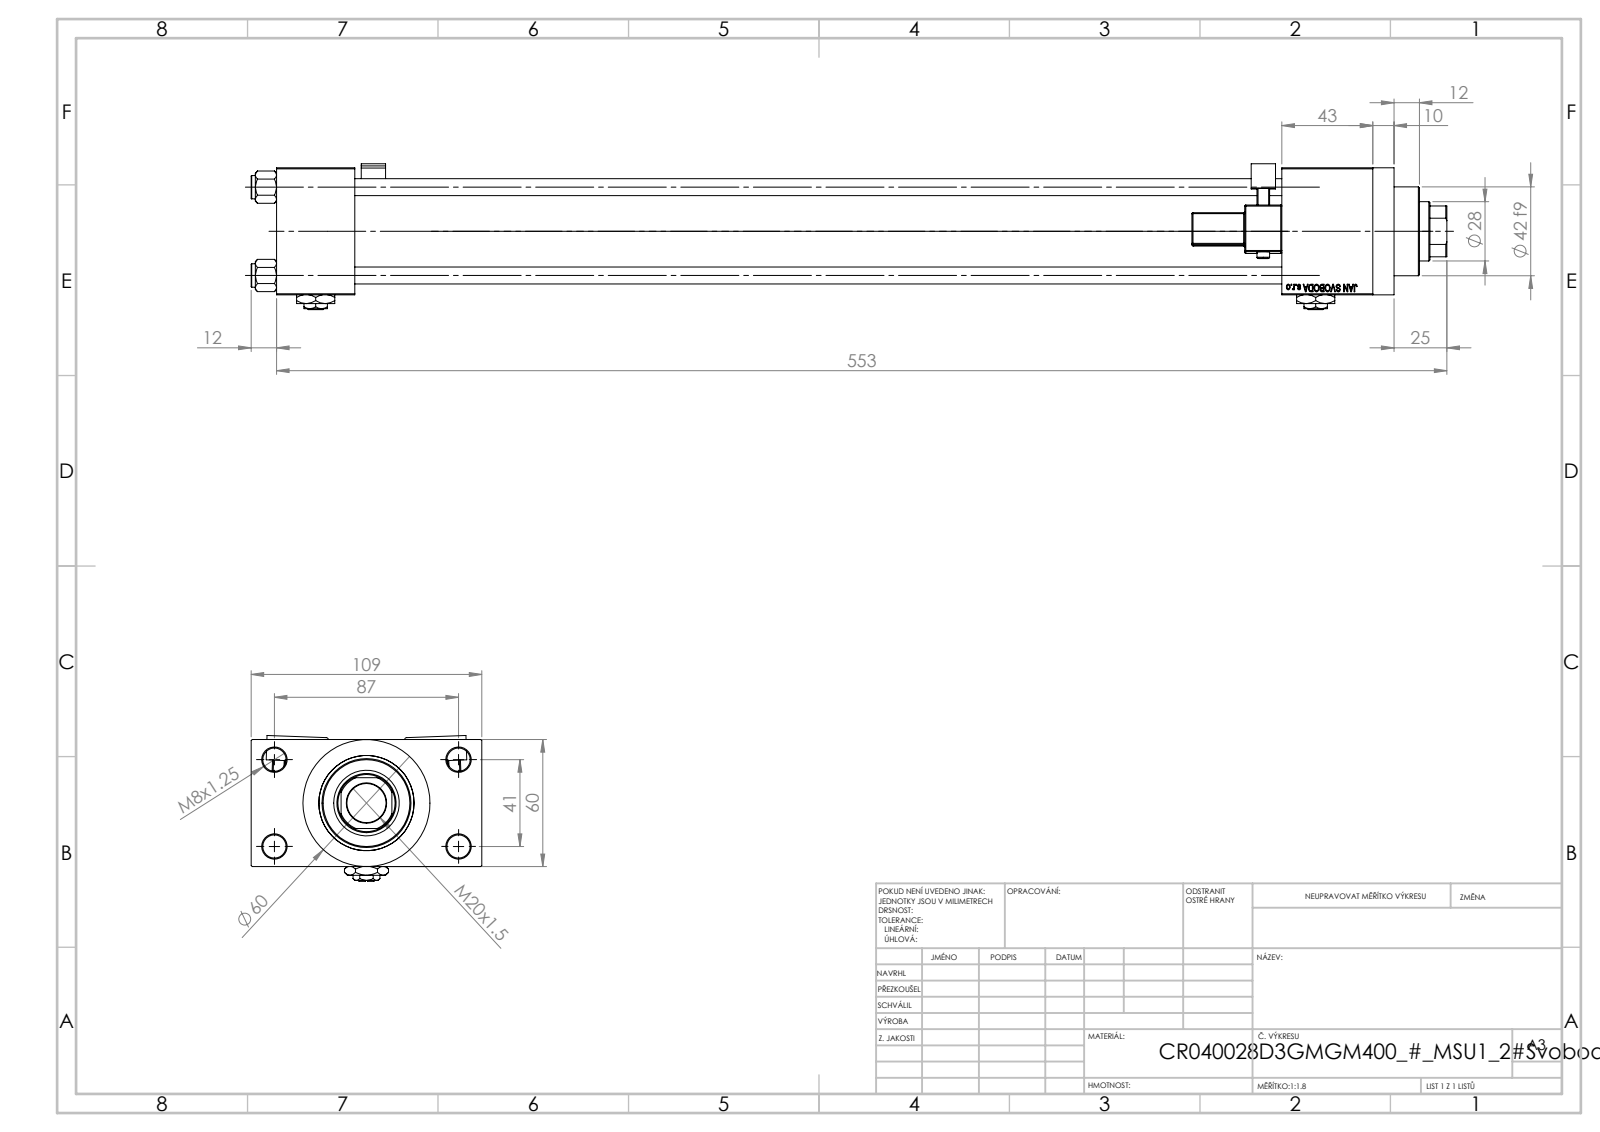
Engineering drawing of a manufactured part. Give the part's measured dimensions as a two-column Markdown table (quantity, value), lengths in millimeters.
| quantity | value |
| --- | --- |
| part name | V215CR_D_Body; NUT_M5_D; Zatka_pro_OIL_PORT; V215CR_MSU (+3 more) |
| STEP written by | SolidWorks 2019 (CONFIG_CONTROL_DESIGN) |
| units | millimeters |
| bodies | 15 solids, 1359 faces (604 planar, 159 cylindrical, 596 other) |
| overall size | 565 × 109 × 68.9 |
| volume | 1 032 000 mm³ |
| surface area | 318 046 mm² |
| round holes (diameter × count) | 8 × 4, 11 × 4, 16.66 × 4, 24 × 4, 7 × 3, 18.5 × 1, 28 × 1, 31 × 1, 40 × 1, 45 × 1 |
| round bosses / shafts (diameter × count) | 11 × 4, 6 × 2, 60 × 1, 46 × 1, 42 × 1 |
| partial cylindrical surfaces (radius × count) | 0.5 × 48, 1 × 2, 2.5 × 2, 4 × 2, 13.5 × 1 |
| main face-to-face distances | 60, 438, 24.5, 84.5, 37, 475, 518, 481, 43, 109 |
| hole center spacings | 22.65, 29.49, 41.7, 47.15, 48.09, 64.35, 76.49, 41 |
